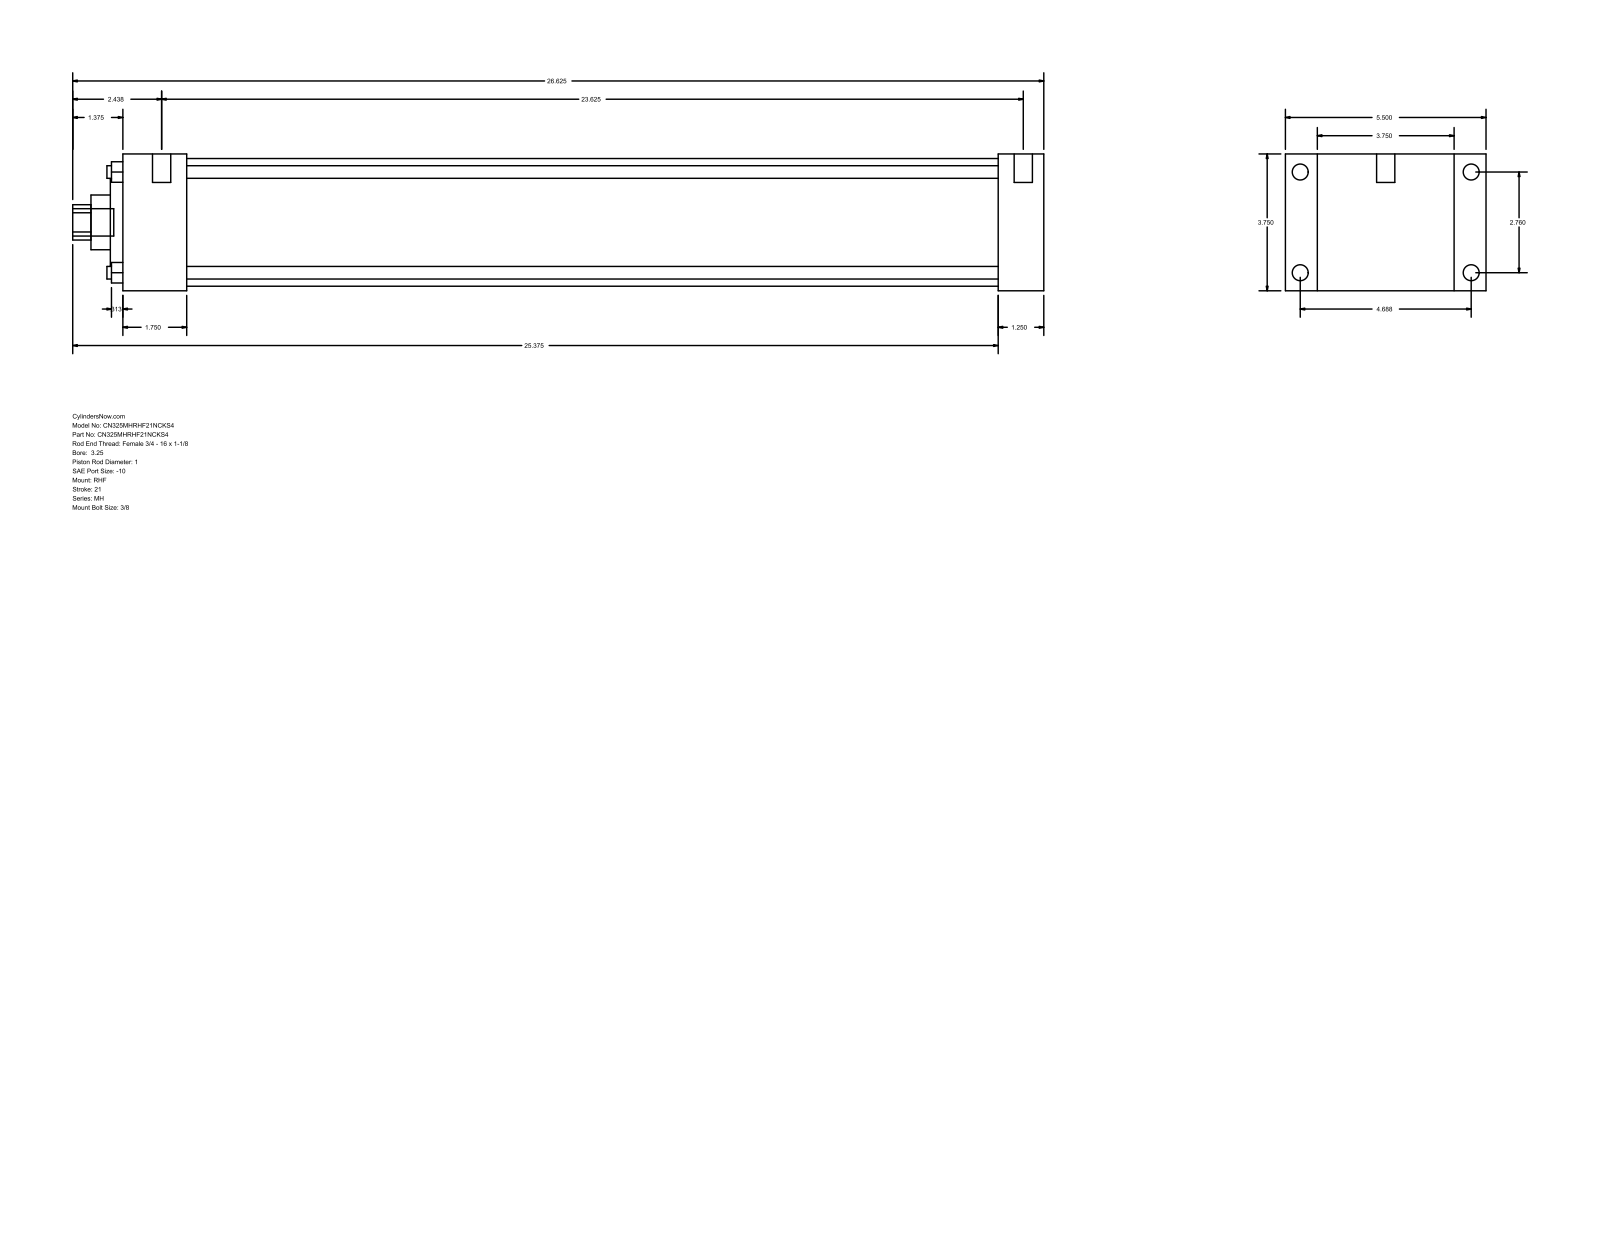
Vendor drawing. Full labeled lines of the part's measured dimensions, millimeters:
Part name (STEP PRODUCT): MH_RHF__0325_1
STEP written by: GSSL Pune (CONFIG_CONTROL_DESIGN)
Units: millimetres
Bodies: 0 solids, 90 faces (61 planar, 29 cylindrical, 0 other)
Overall size (bounding box): 676.27 × 139.7 × 95.25
Round holes (diameter × count): ⌀8.76 ×4, ⌀25.4 ×1, ⌀38.1 ×1, ⌀60.33 ×1, ⌀88.9 ×1
Round bosses / shafts (diameter × count): ⌀11.13 ×4, ⌀5.56 ×4, ⌀12.7 ×2, ⌀19.05 ×1
Partial cylindrical surfaces — rounded edges, fillets, slot ends (radius × count): R12.29 ×1
Main face-to-face distances: 95.24, 31.75, 22.23, 117.47, 609.6, 641.35, 139.7, 44.46, 565.14, 596.89
Hole centre spacings: 49.57, 70.1, 99.14
